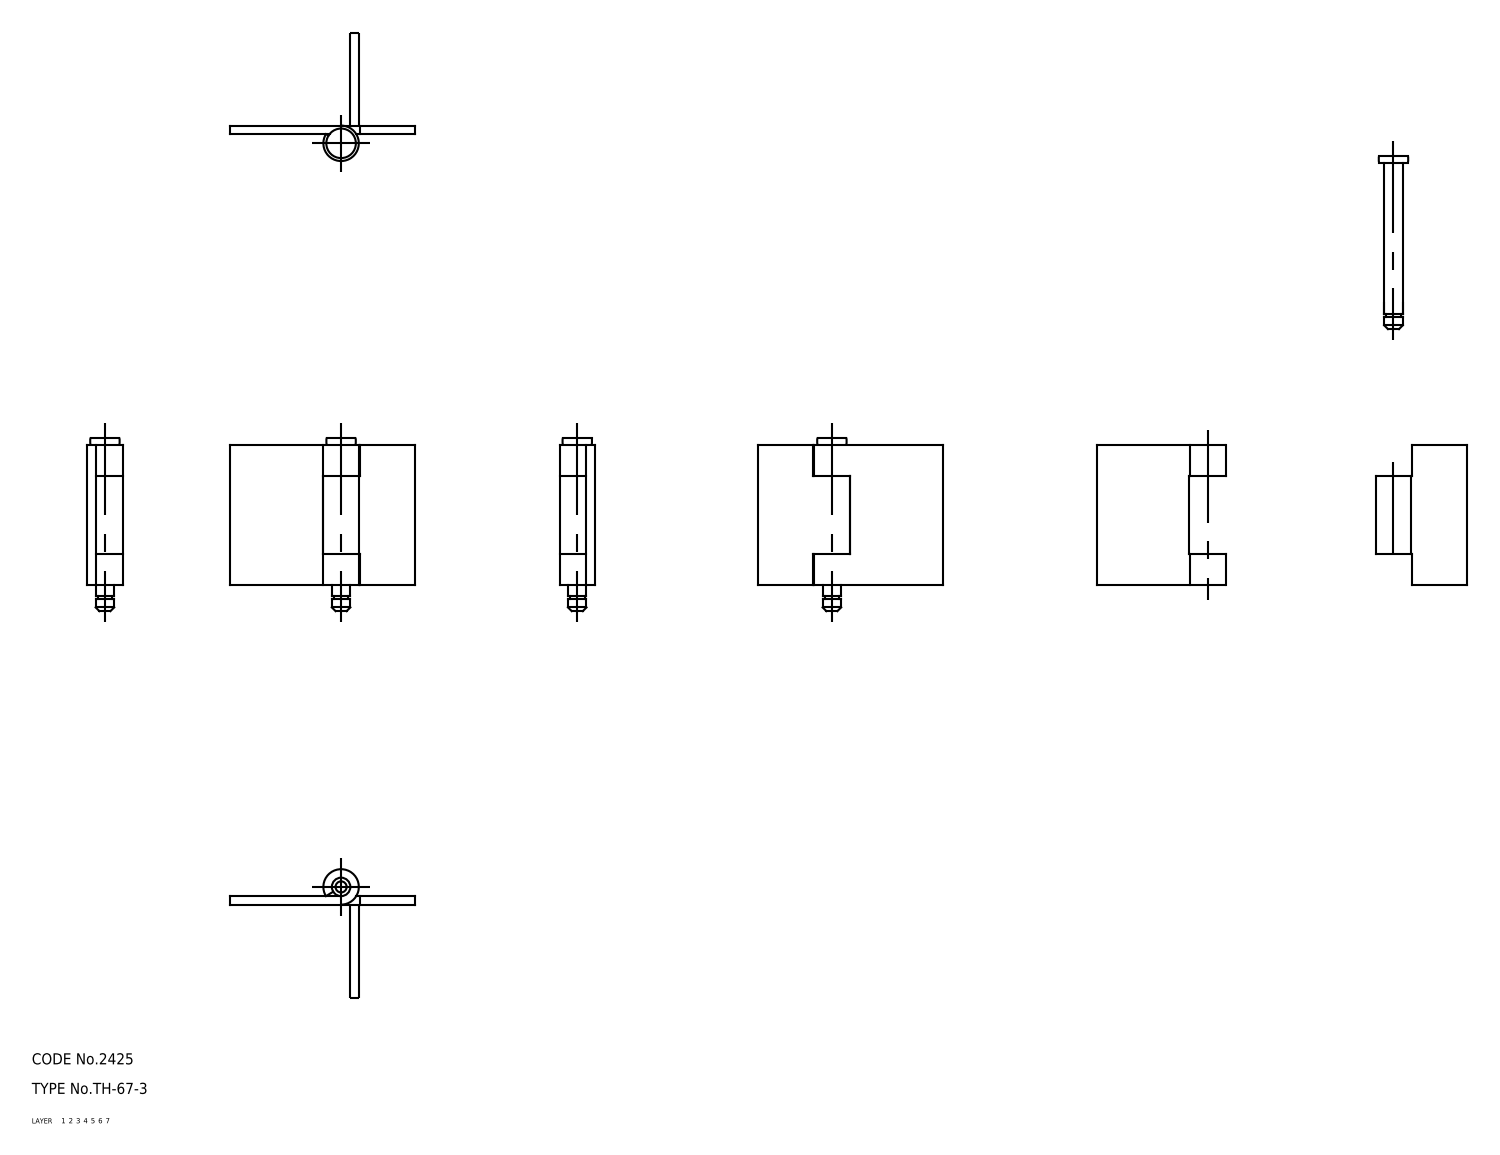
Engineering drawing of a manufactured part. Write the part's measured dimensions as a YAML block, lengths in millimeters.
part_name: "shaft; hinge piece_B; hinge piece_A; TH_67_3_13839_36"
step_written_by: "CADfix (AUTOMOTIVE_DESIGN)"
units: millimeters
bodies: {solids: 3, faces: 40, planar: 0, cylindrical: 0, other: 40}
overall_size: [50, 47, 9.6]
volume: 6579
surface_area: 6596
